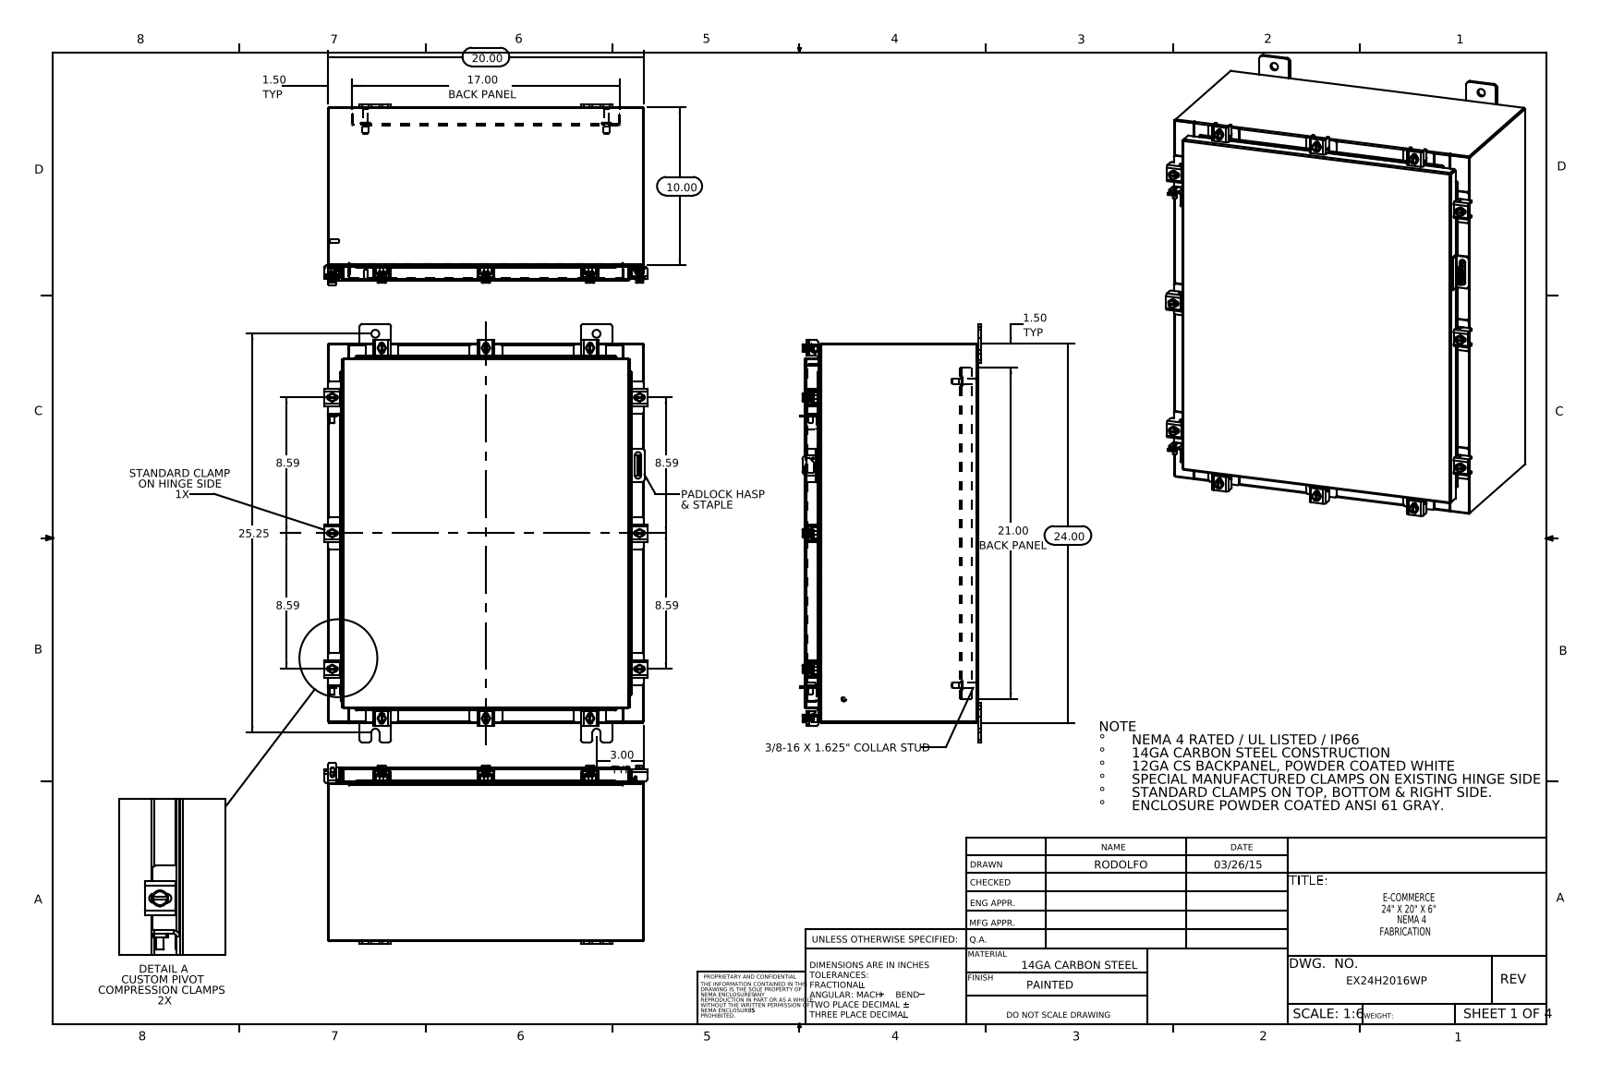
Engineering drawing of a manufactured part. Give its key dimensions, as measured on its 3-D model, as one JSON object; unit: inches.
{"part_name": "ATEX CLAMP HINGE BRAKET; EX24H2016WP Backpanel; EX24H2016WP Bottom; N-WMT04X30402202210-00 22101002 (+8 more)", "step_written_by": "SolidWorks 2014 (AUTOMOTIVE_DESIGN)", "units": "inches", "bodies": {"solids": 81, "faces": 2018, "planar": 1075, "cylindrical": 783, "other": 160}, "overall_size": [26.5, 20.421, 11.453], "volume_in3": 200.3, "surface_area_in2": 5038, "round_holes": [[0.213, 12], [0.26, 12], [0.5, 8], [0.125, 1], [0.25, 1]], "round_bosses_or_shafts": [[0.5, 12], [0.25, 12], [0.399, 10], [0.625, 4], [0.375, 4], [0.33, 4], [0.315, 2], [0.236, 2]], "partial_cylinders_radius": [[0.06, 54], [0.013, 24], [0.141, 24], [0.19, 24], [0.088, 22], [0.12, 22], [0.09, 18], [0.05, 17]], "face_to_face_distances": [0.075, 10.9, 19.925, 10.975, 10.826, 23.925, 0.104, 1, 1.075, 9.826], "hole_center_spacings": [2.34, 4.429, 6.594, 8.594, 10.217, 12.137, 15.234, 16.617]}
